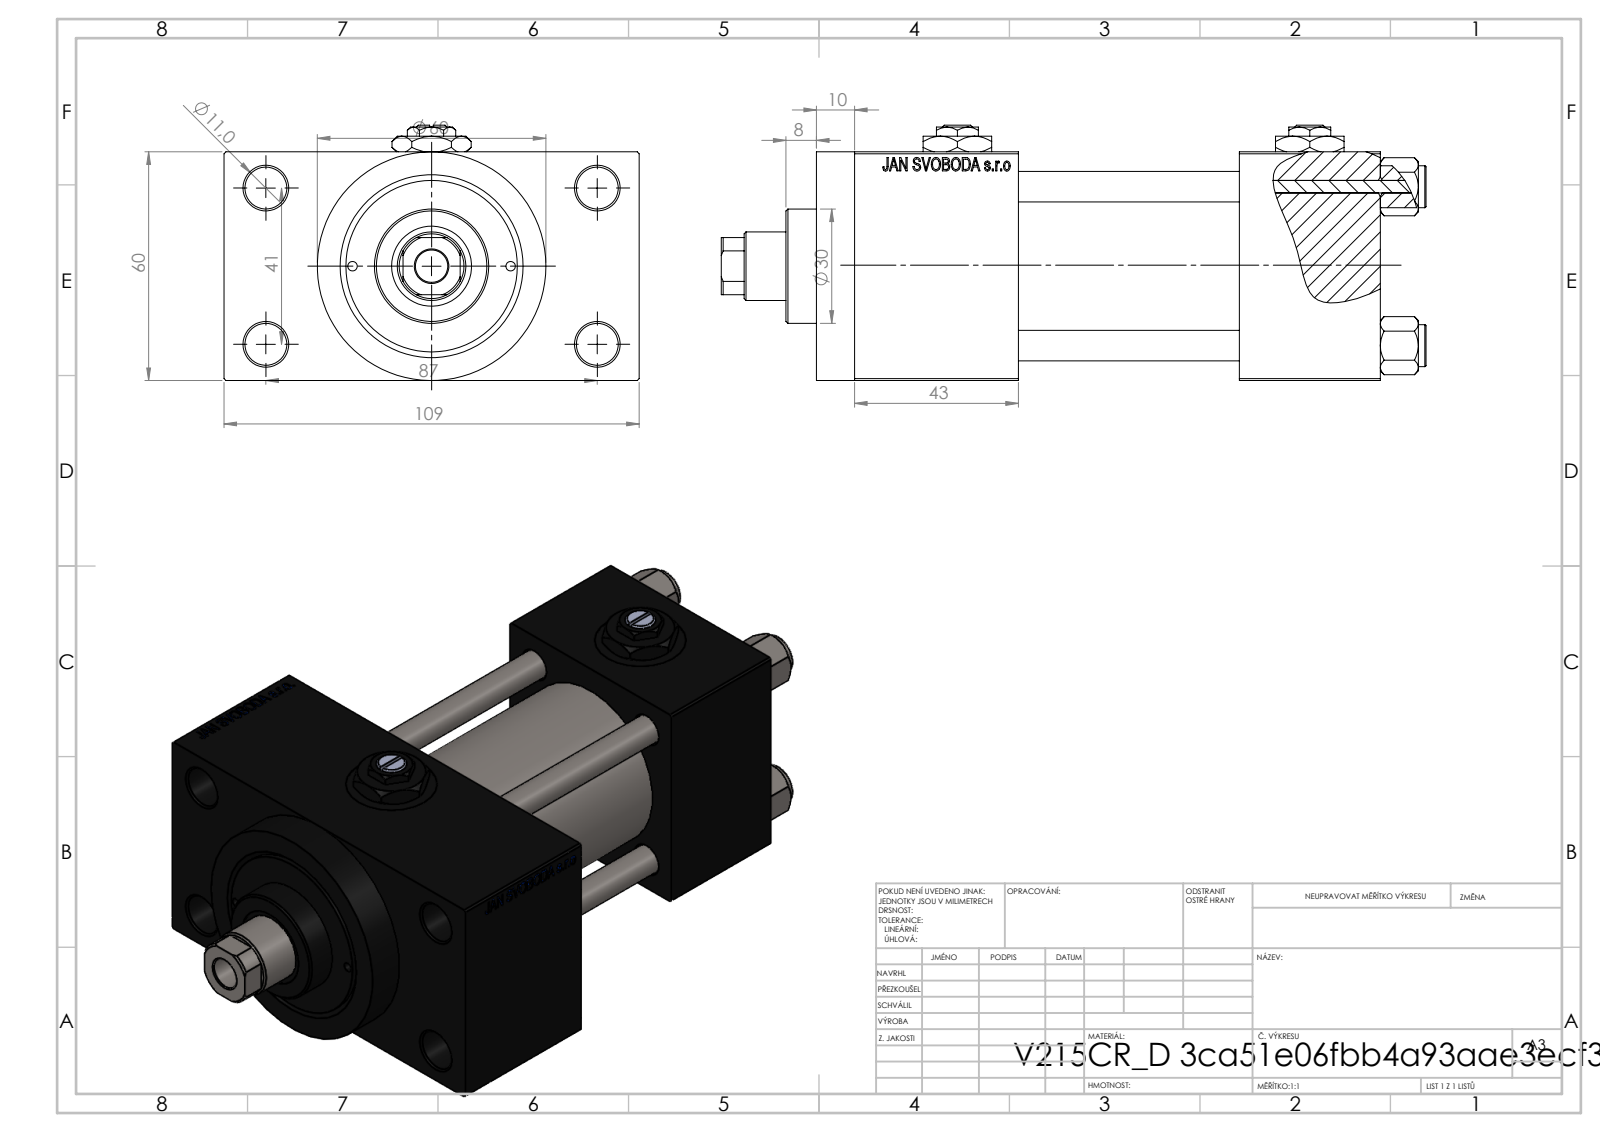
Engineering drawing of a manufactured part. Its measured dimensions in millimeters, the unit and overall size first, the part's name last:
Units: millimetres
Overall size (bounding box): 185 × 109 × 67
Round holes (diameter × count): ⌀8 ×4, ⌀11 ×4, ⌀16.66 ×4, ⌀24 ×4, ⌀7 ×3, ⌀2.5 ×2, ⌀8.5 ×1, ⌀18 ×1, ⌀21 ×1, ⌀31 ×1, ⌀40 ×1, ⌀45 ×1
Round bosses / shafts (diameter × count): ⌀11 ×4, ⌀60 ×1, ⌀46 ×1, ⌀30 ×1
Partial cylindrical surfaces — rounded edges, fillets, slot ends (radius × count): R8.5 ×1
Main face-to-face distances: 60, 58, 24.5, 84.5, 37, 95, 43, 138, 101, 10
Hole centre spacings: 20.85, 22.65, 29.49, 30.62, 41.7, 46.53, 47.15, 48.09
Volume: 510 125 mm³ · Surface area: 125 149 mm²
Bodies: 13 solids, 1213 faces (548 planar, 103 cylindrical, 562 other)
Part name (STEP PRODUCT): Zatka_pro_OIL_PORT; NUT_M5_D; V215_VC_A; V215CR_D_Body (+2 more)
STEP written by: SolidWorks 2019 (CONFIG_CONTROL_DESIGN)
